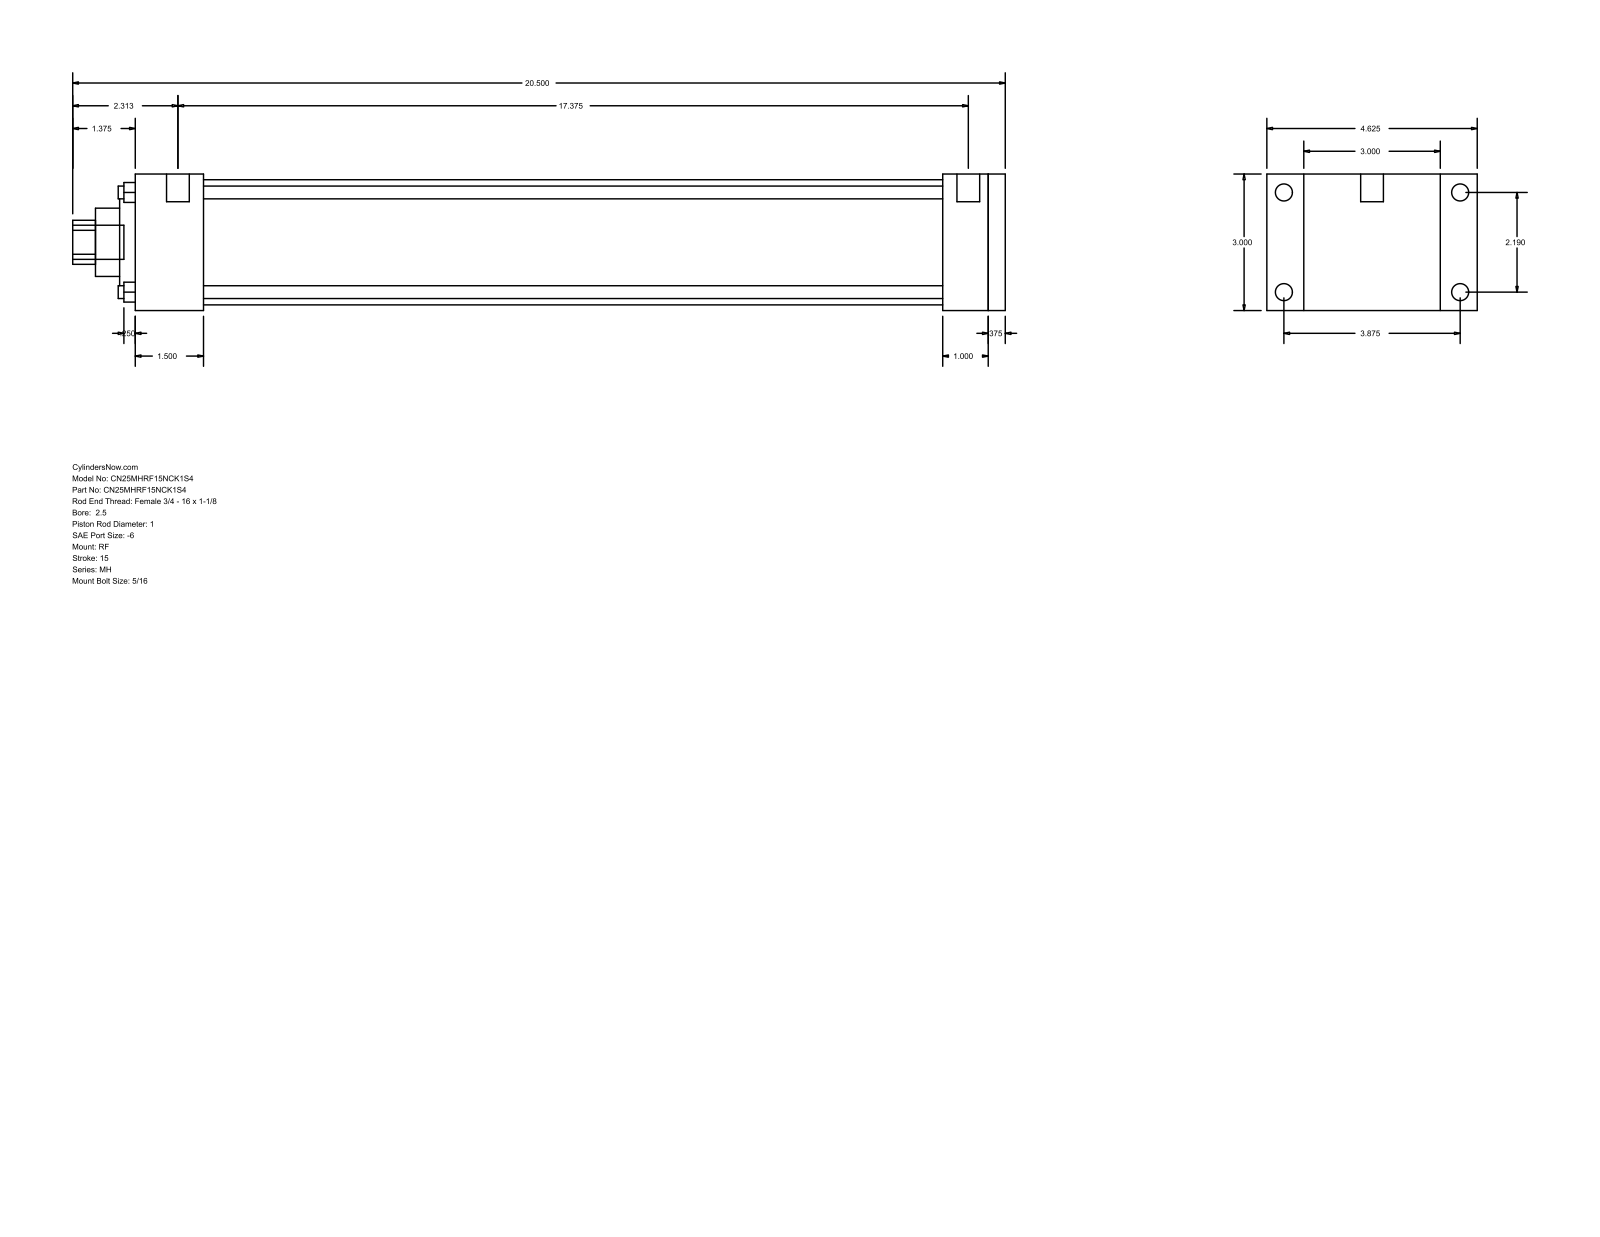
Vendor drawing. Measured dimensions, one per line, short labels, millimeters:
name: MH_RF__0250_1
written by: GSSL Pune (CONFIG_CONTROL_DESIGN)
unit: mm
bodies: 0 solids, 94 faces (65 planar, 29 cylindrical, 0 other)
size: 520.7 × 117.47 × 76.2
holes: 4× ⌀7.14, 1× ⌀25.4, 1× ⌀38.1, 1× ⌀60.33, 1× ⌀69.85
bosses: 4× ⌀9.53, 4× ⌀5.56, 2× ⌀12.7, 1× ⌀19.05
rounds: 1× R12.29
face distances: 76.2, 9.52, 485.78, 476.26, 450.85, 25.41, 34.93, 38.11, 412.74, 438.15
hole spacings: 39.33, 55.62, 78.66
